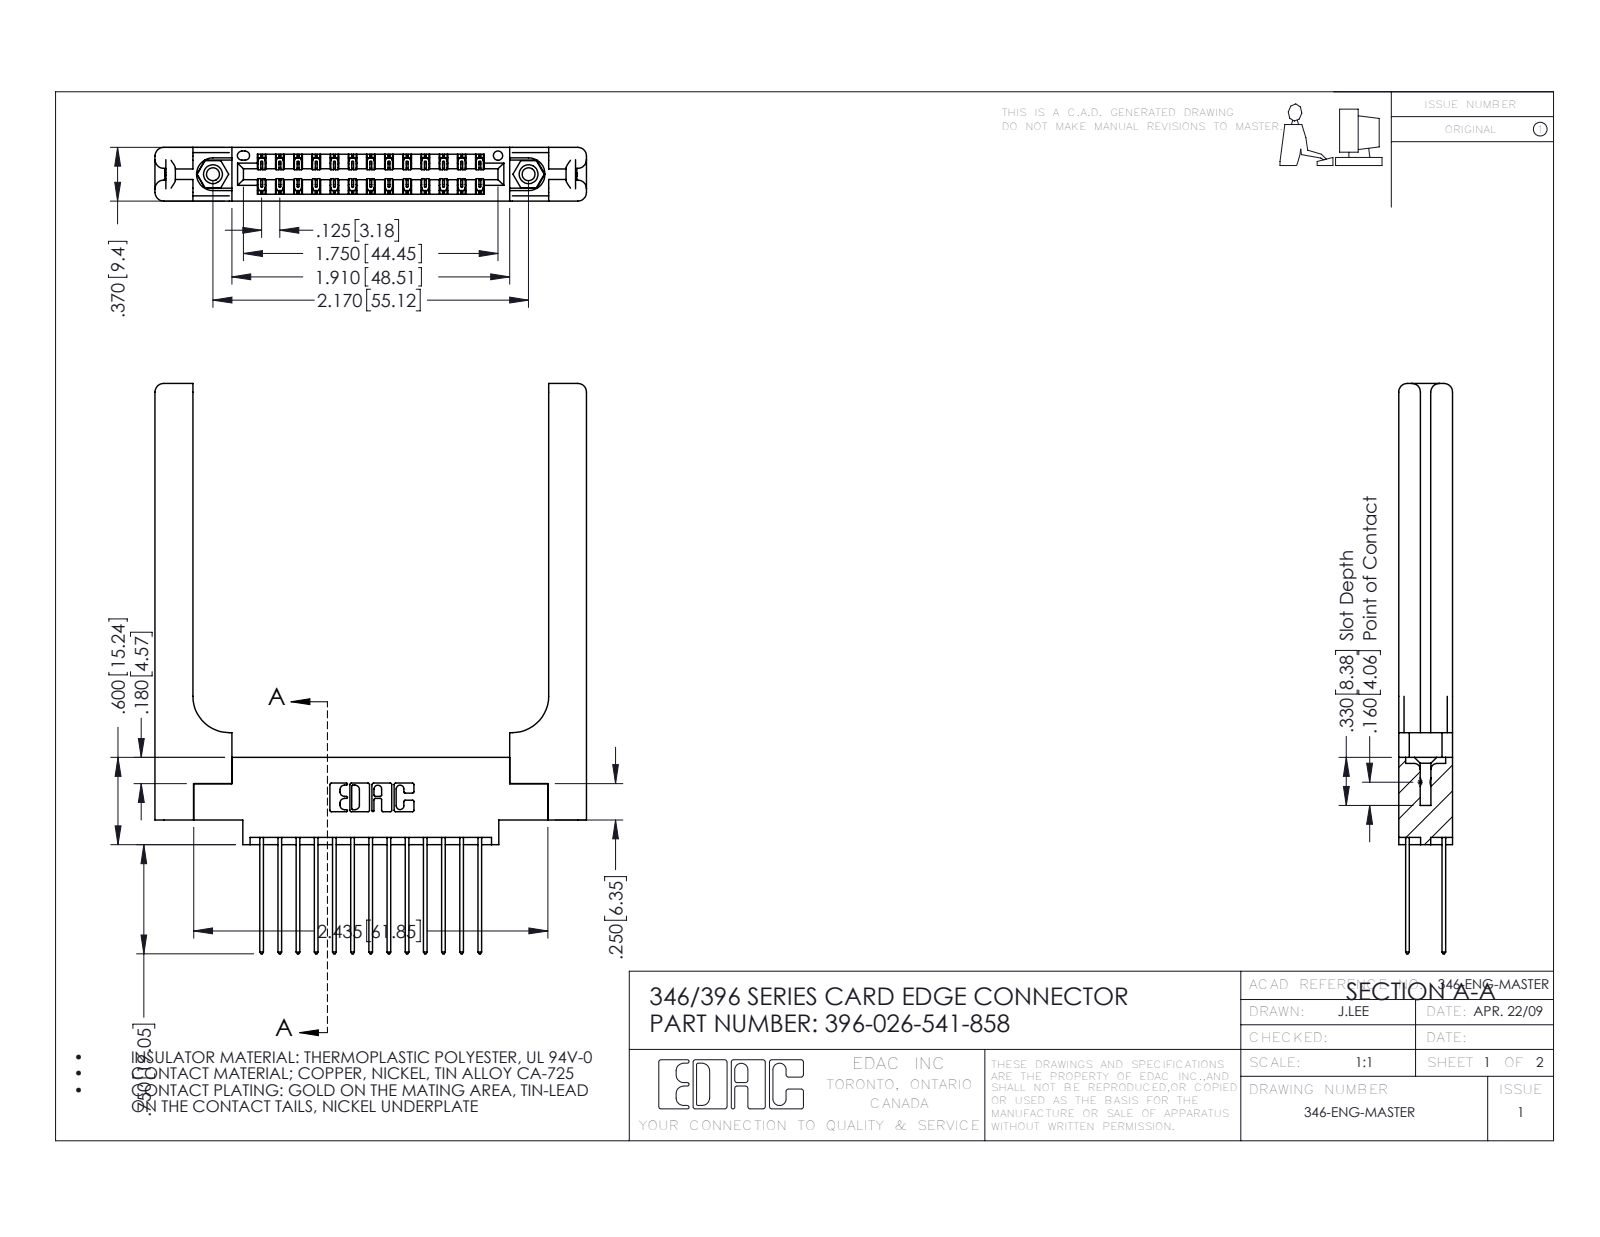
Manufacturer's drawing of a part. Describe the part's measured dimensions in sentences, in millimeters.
The part is named "346 Part_0.170 Offset - 0.156 Dia-TH; 345-292-001_345-293-141; 396-026-541-858; 345-250-001_345-250-001-102 (+1 more)". Its 3-D file was written by "SolidWorks 2016 (CONFIG_CONTROL_DESIGN)". It is 31 solids with 1734 faces: 1138 planar, 536 cylindrical and 60 other. Overall it measures 99.6 by 75.3 by 9.4 millimeters. Its volume is 14 600 cubic millimeters and its surface area 15 190 square millimeters. Round holes: 2 of diameter 2.3, 2 of diameter 3.2, 2 of diameter 4, 1 of diameter 1.6. Round bosses or shafts: 2 of diameter 3.9. Partial cylindrical surfaces (rounded edges, fillets, slot ends): 39 of radius 0.2, 26 of radius 0.3, 22 of radius 0.3, 16 of radius 1.5, 6 of radius 0.2, 6 of radius 0.8, 3 of radius 0.7, 2 of radius 0.4. The main face-to-face distances are 9.4, 1.8, 1.2, 8.2, 3.8, 3.8, 6.4, 0.6, 7.6, 2. The hole center spacings are 6.2, 49.9, 55.1.
